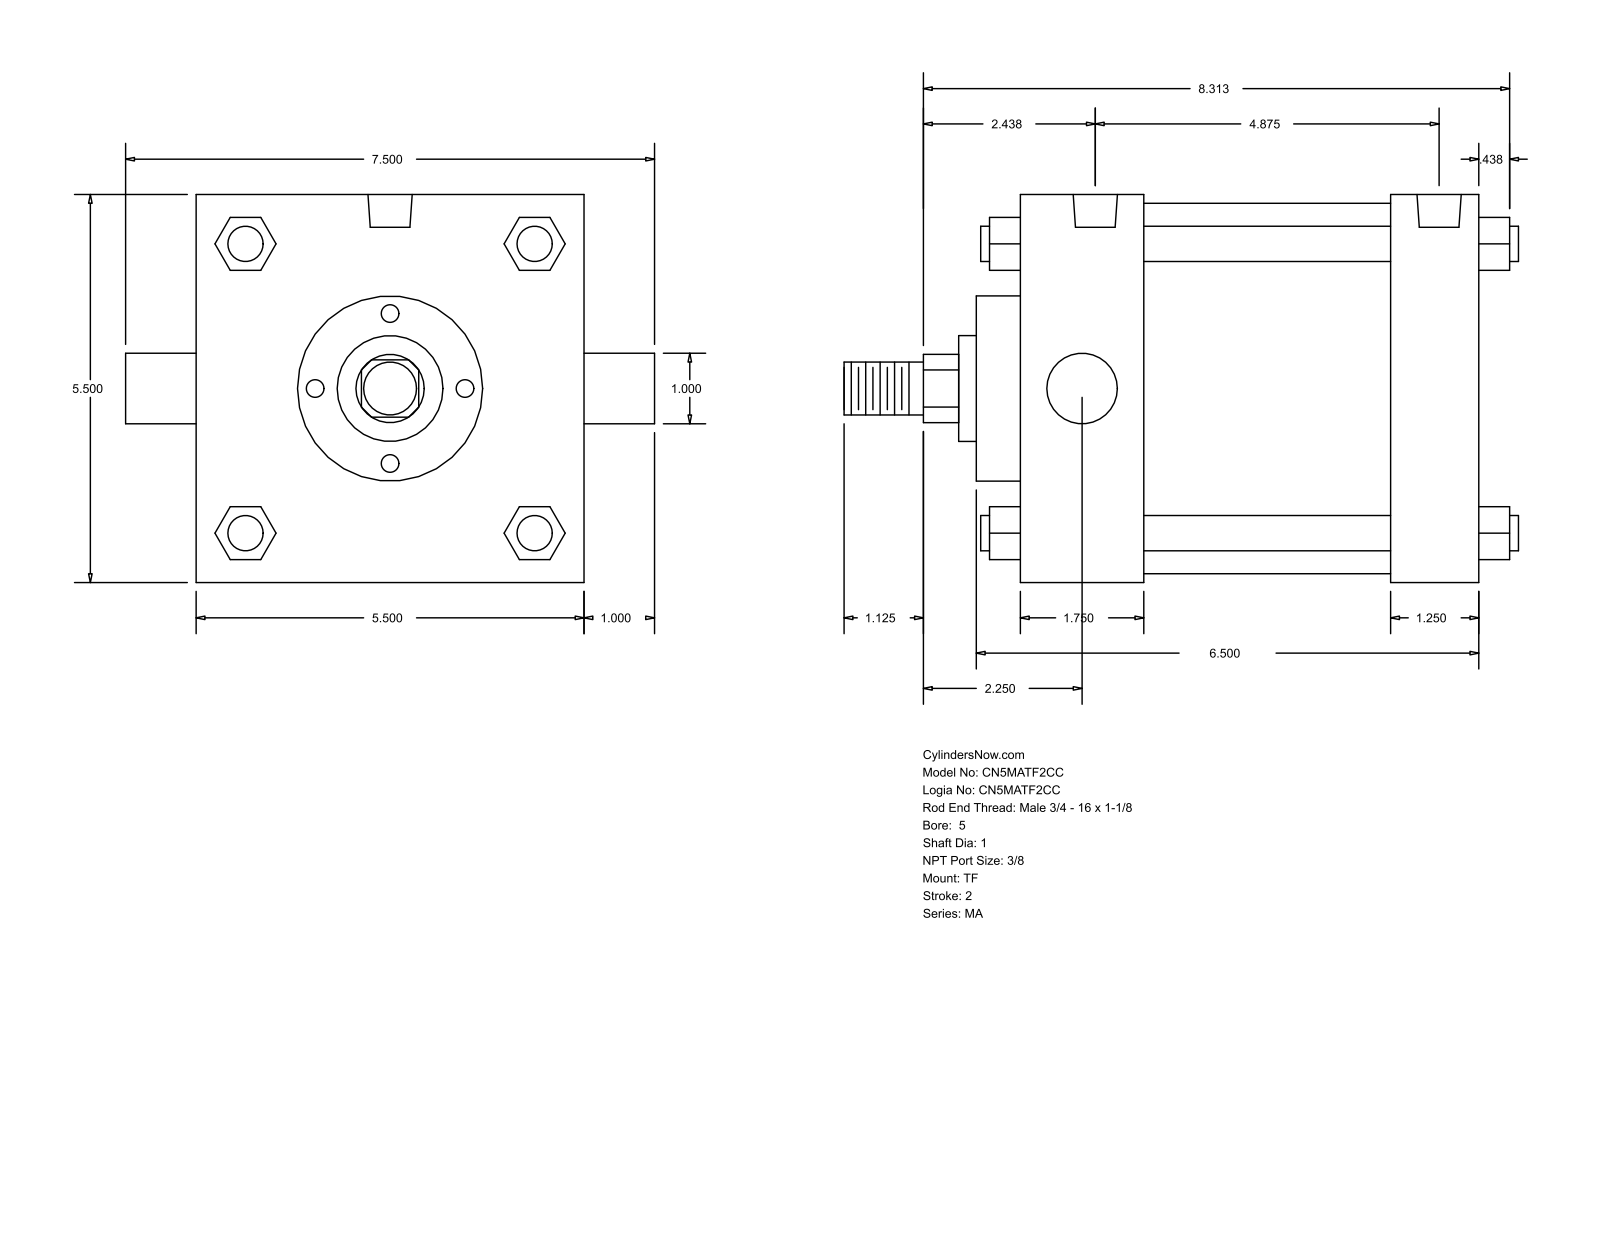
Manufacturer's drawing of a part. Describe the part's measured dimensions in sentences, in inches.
The part is named "MA_TF__0500_1". Its 3-D file was written by "GSSL Pune (CONFIG_CONTROL_DESIGN)". It is 0 solids with 122 faces: 93 planar, 29 cylindrical and 0 other. Overall it measures 9.563 by 7.5 by 5.5 inches. Round holes: 3 of diameter 0.437, 2 of diameter 0.627. Round bosses or shafts: 4 of diameter 0.5, 2 of diameter 1, 1 of diameter 5.25, 1 of diameter 2.625, 1 of diameter 1.5, 1 of diameter 0.75. Partial cylindrical surfaces (rounded edges, fillets, slot ends): 1 of radius 0.484. The main face-to-face distances are 5.5, 6.5, 5.25, 1.25, 1.75, 3.5, 4.75, 0.625, 2.375, 5.875. The hole center spacings are 0.187, 0.188, 4.5, 4.687, 4.688, 4.875.
